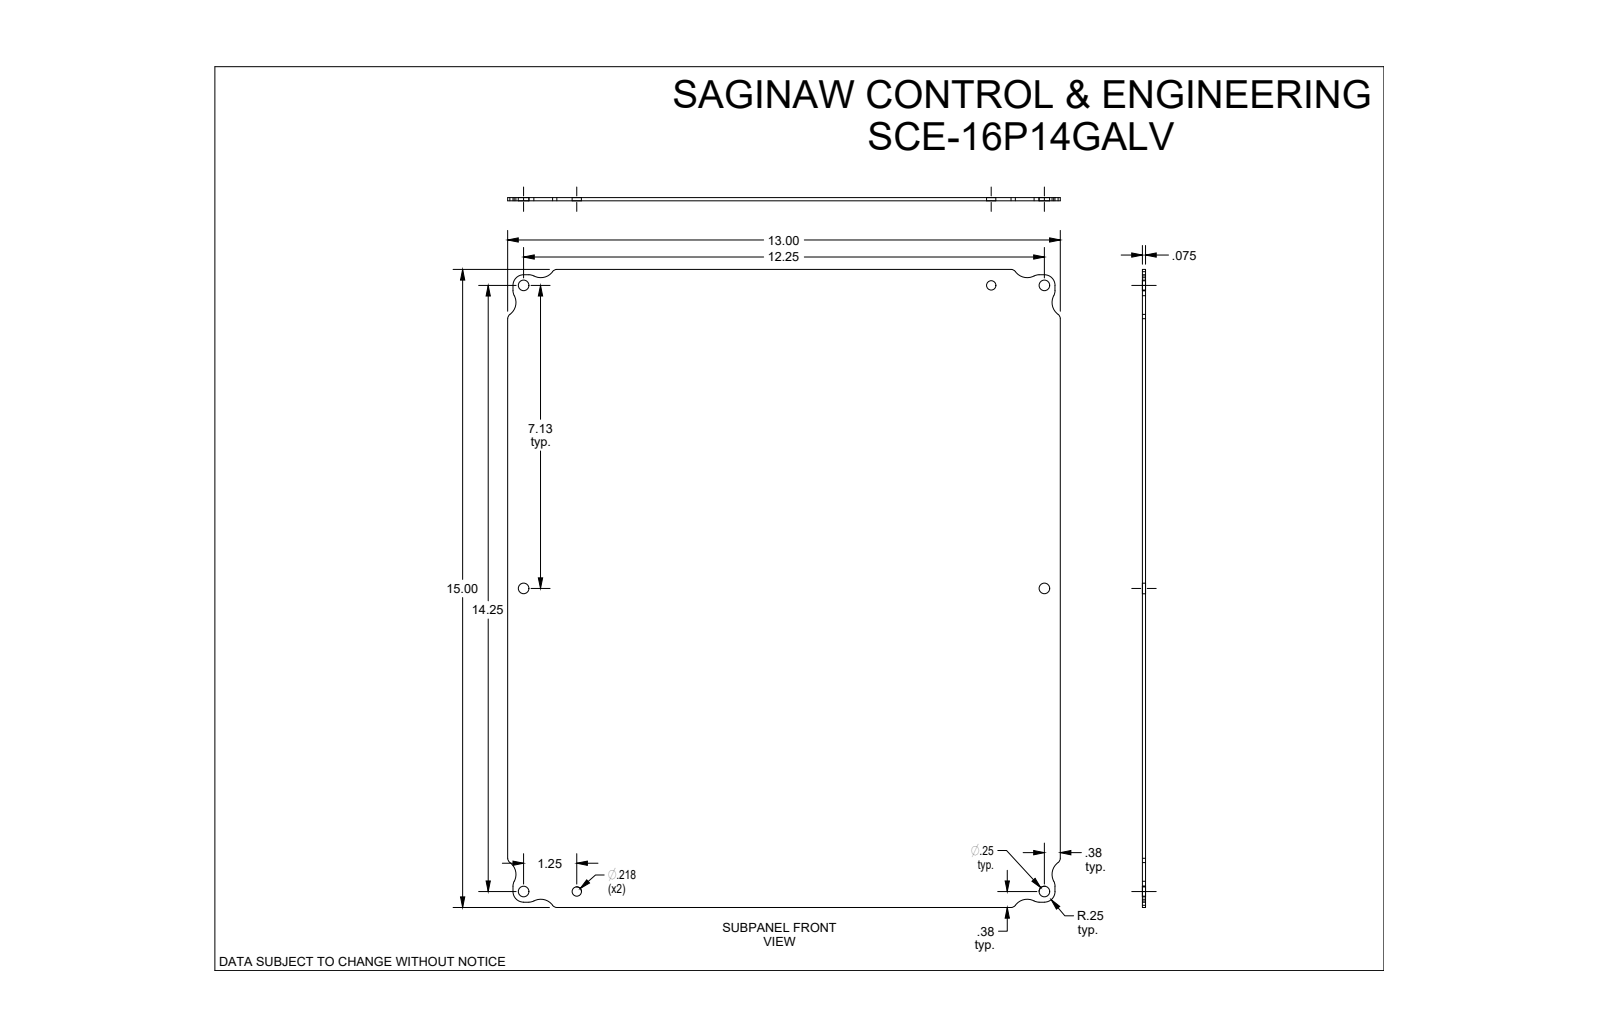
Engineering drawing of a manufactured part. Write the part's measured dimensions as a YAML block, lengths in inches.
part_name: "SCE-16P14GALV"
step_written_by: "SolidWorks 2019 (CONFIG_CONTROL_DESIGN)"
units: inches
bodies: {solids: 1, faces: 50, planar: 14, cylindrical: 36, other: 0}
overall_size: [15, 13, 0.075]
volume: 14.51
surface_area: 391.5
round_holes:
  - {diameter: 0.25, count: 6}
  - {diameter: 0.218, count: 2}
partial_cylinders:
  - {radius: 0.25, count: 12}
  - {radius: 0.125, count: 8}
  - {radius: 0.344, count: 8}
face_to_face_distances: [0.075, 13, 15, 0.125, 14.875, 12.875, 14.75, 12.75]
hole_center_spacings: [7.125, 14.171, 12.25, 1.25, 7.233, 11, 13.106, 14.25]
